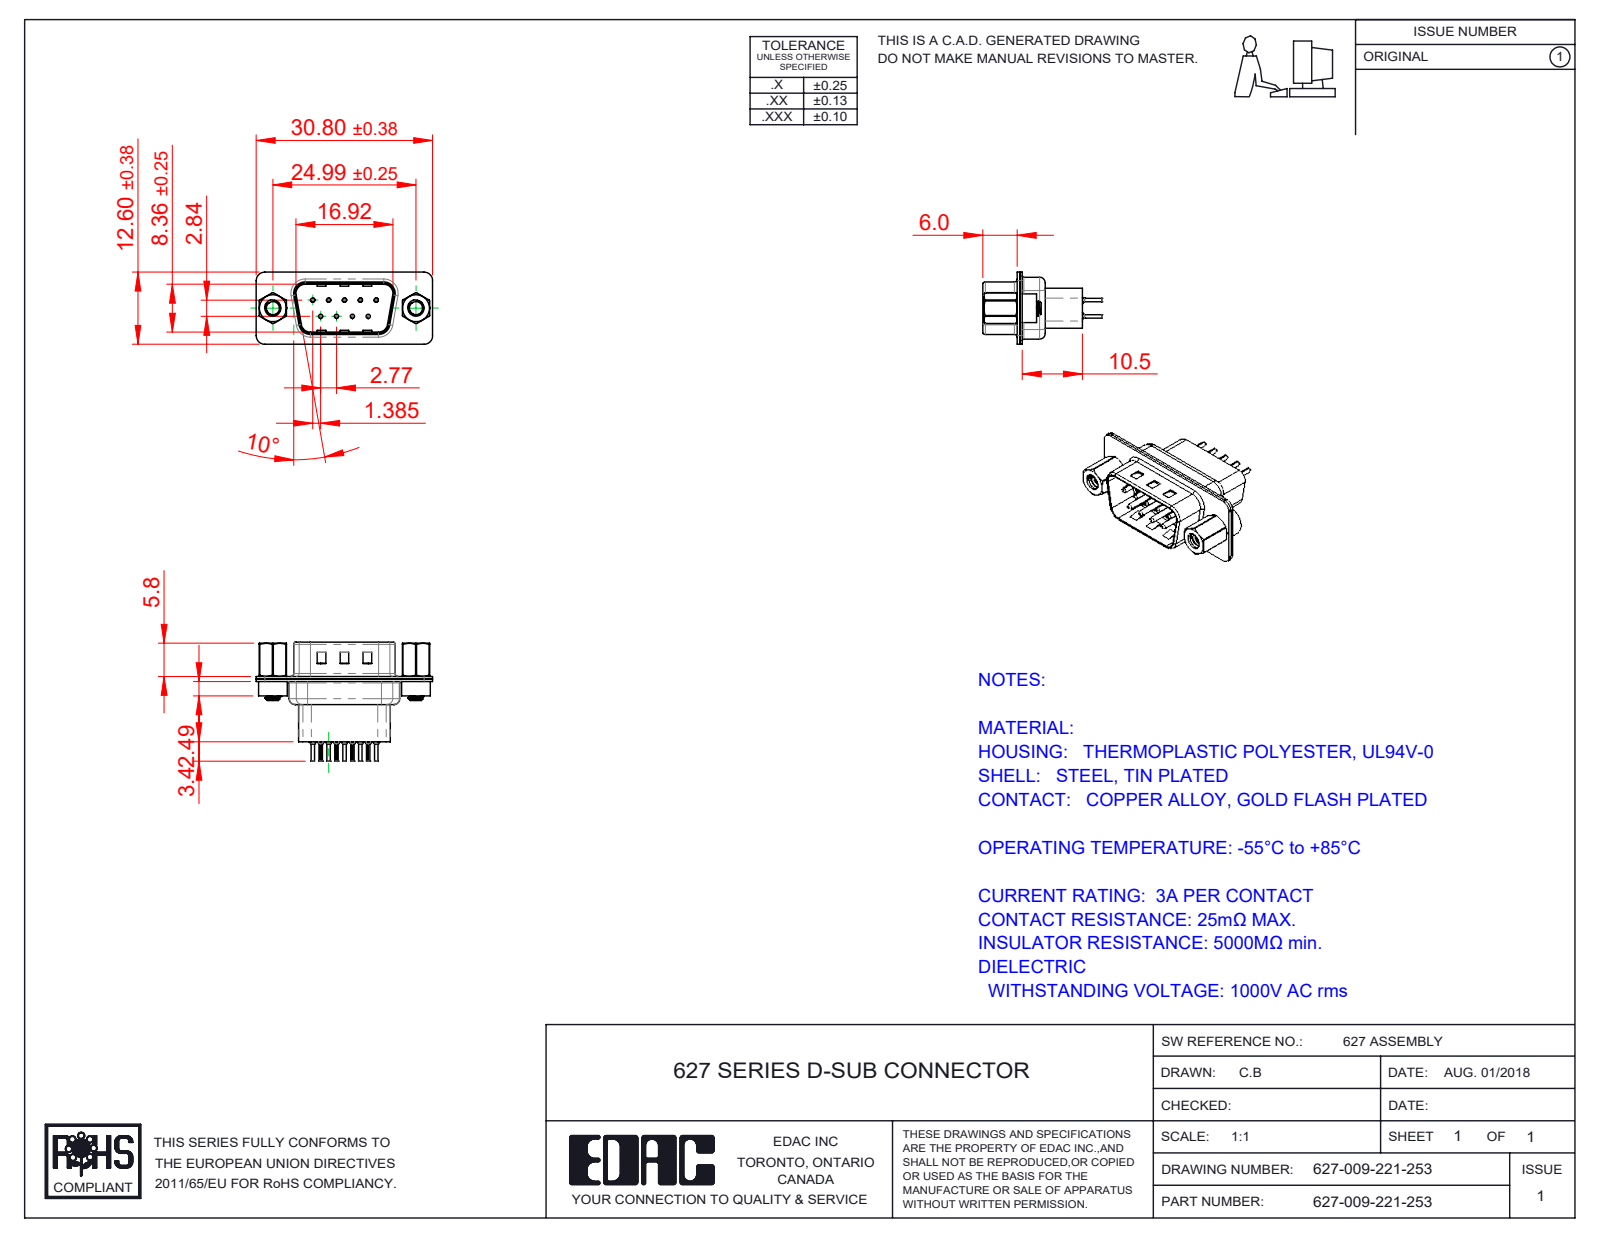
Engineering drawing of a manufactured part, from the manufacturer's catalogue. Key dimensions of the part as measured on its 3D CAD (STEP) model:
Part name (STEP PRODUCT): 627 Contact Row 1_21H; 627 Shell Front_09 Contacts; 627 4-40 Threaded Rivet; 627 Shell Rear_09 Contacts (+4 more)
STEP written by: SolidWorks 2020 (CONFIG_CONTROL_DESIGN)
Units: millimetres
Bodies: 16 solids, 1308 faces (345 planar, 532 cylindrical, 431 other)
Overall size (bounding box): 30.8 × 20.8 × 12.6
Volume: 1 979 mm³ · Surface area: 5 171 mm²
Round holes (diameter × count): ⌀0.2 ×9, ⌀0.35 ×9, ⌀1.1 ×9, ⌀1.6 ×9, ⌀2.26 ×2, ⌀2.29 ×2, ⌀4 ×2, ⌀4.8 ×2
Round bosses / shafts (diameter × count): ⌀2 ×9, ⌀1.5 ×9, ⌀0.75 ×9, ⌀0.6 ×9, ⌀5 ×2, ⌀4.9 ×2, ⌀2.79 ×2
Partial cylindrical surfaces — rounded edges, fillets, slot ends (radius × count): R0.1 ×18, R1.5 ×18, R2 ×12, R0.5 ×8, R1.6 ×8, R0.25 ×4, R0.6 ×4, R0.65 ×4
Main face-to-face distances: 0.45, 0.4, 0.9, 0.82, 9.58, 1.4, 1.5, 0.68, 7.68, 1.08
Hole centre spacings: 3.16, 2.77, 5.54, 5.03, 5.04, 8.31, 7.48, 7.49
